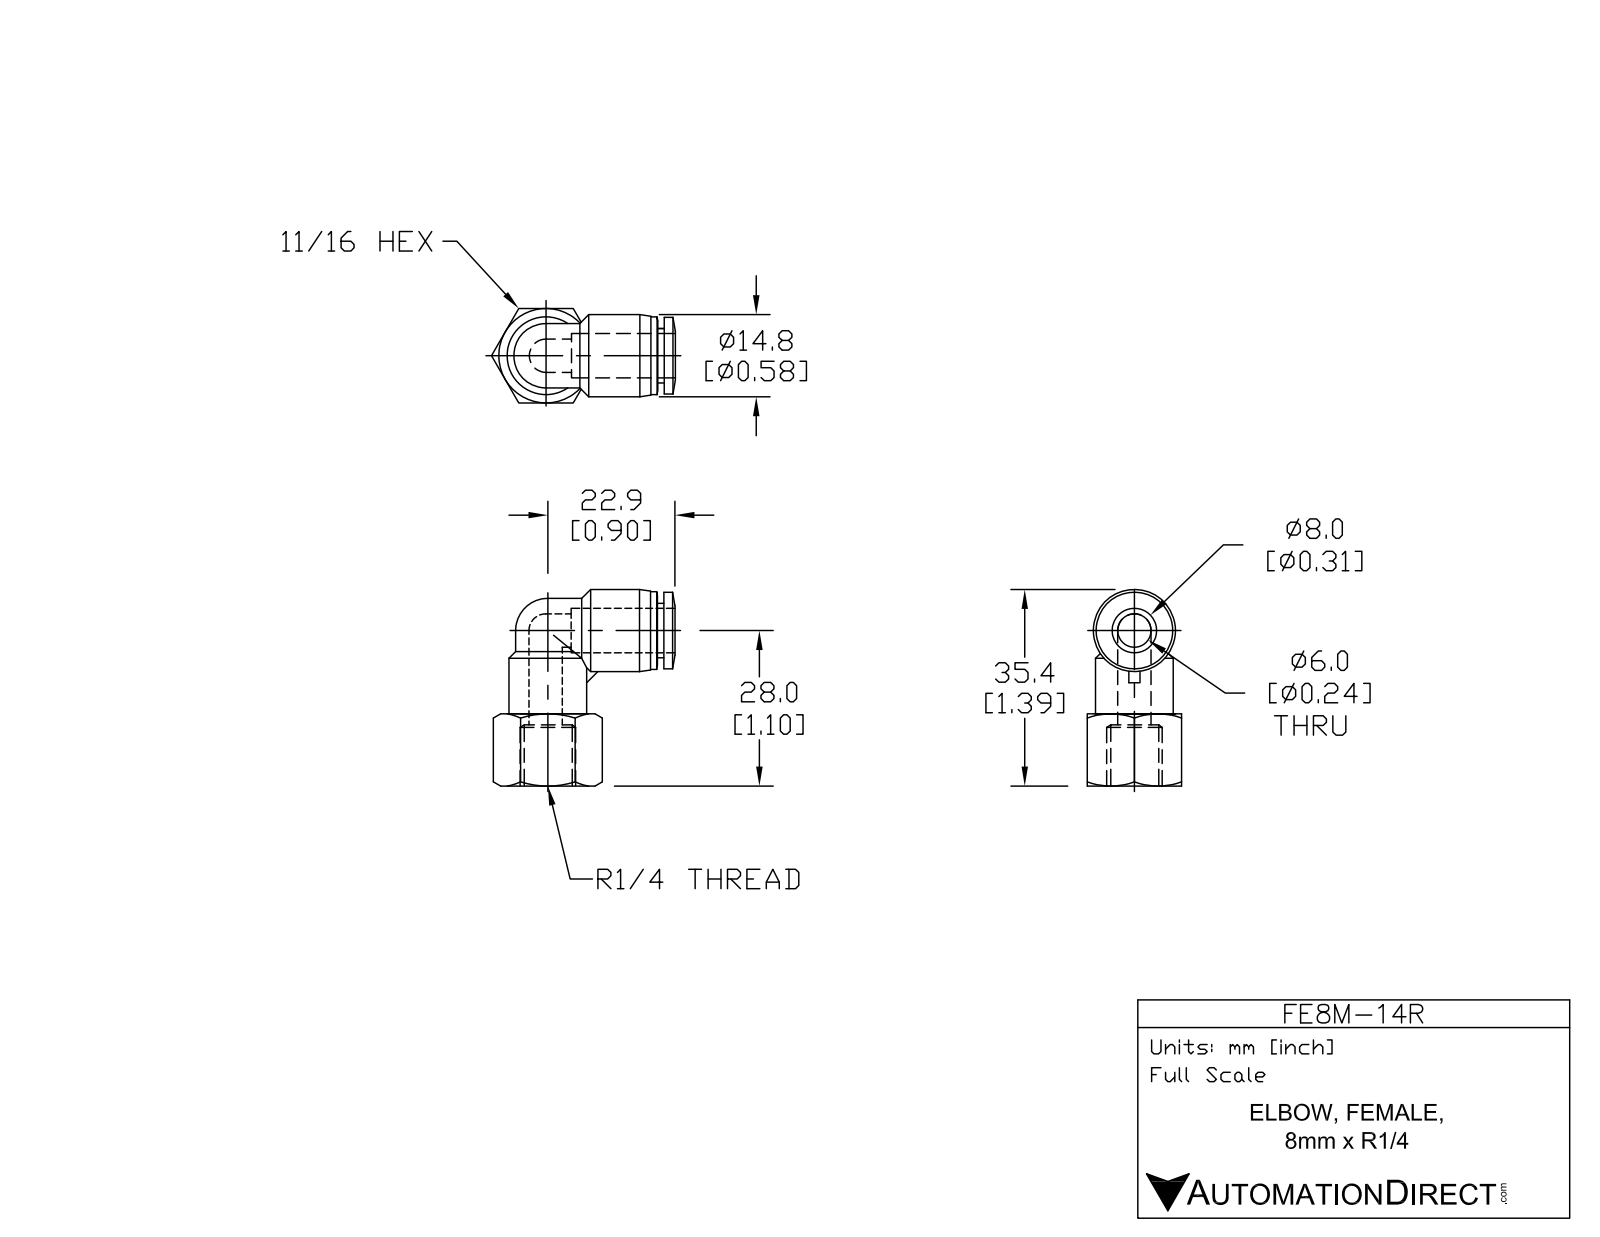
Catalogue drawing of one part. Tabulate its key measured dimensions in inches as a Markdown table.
| quantity | value |
| --- | --- |
| part name | FE8M-14R |
| STEP written by | SolidWorks 2015 (AUTOMOTIVE_DESIGN) |
| units | inches |
| bodies | 1 solid, 67 faces (17 planar, 19 cylindrical, 31 other) |
| overall size | 1.394 × 1.288 × 0.669 |
| volume | 0.338 in³ |
| surface area | 6.529 in² |
| round holes (diameter × count) | 0.236 × 2, 0.327 × 1 |
| round bosses / shafts (diameter × count) | 0.551 × 2, 0.583 × 1, 0.543 × 1, 0.457 × 1, 0.386 × 1 |
| partial cylindrical surfaces (radius × count) | 0.228 × 1 |
| main face-to-face distances | 0.669, 0.433, 0.079, 0.512, 0.045, 0.596, 0.642, 0.72, 0.124, 0.295 |
